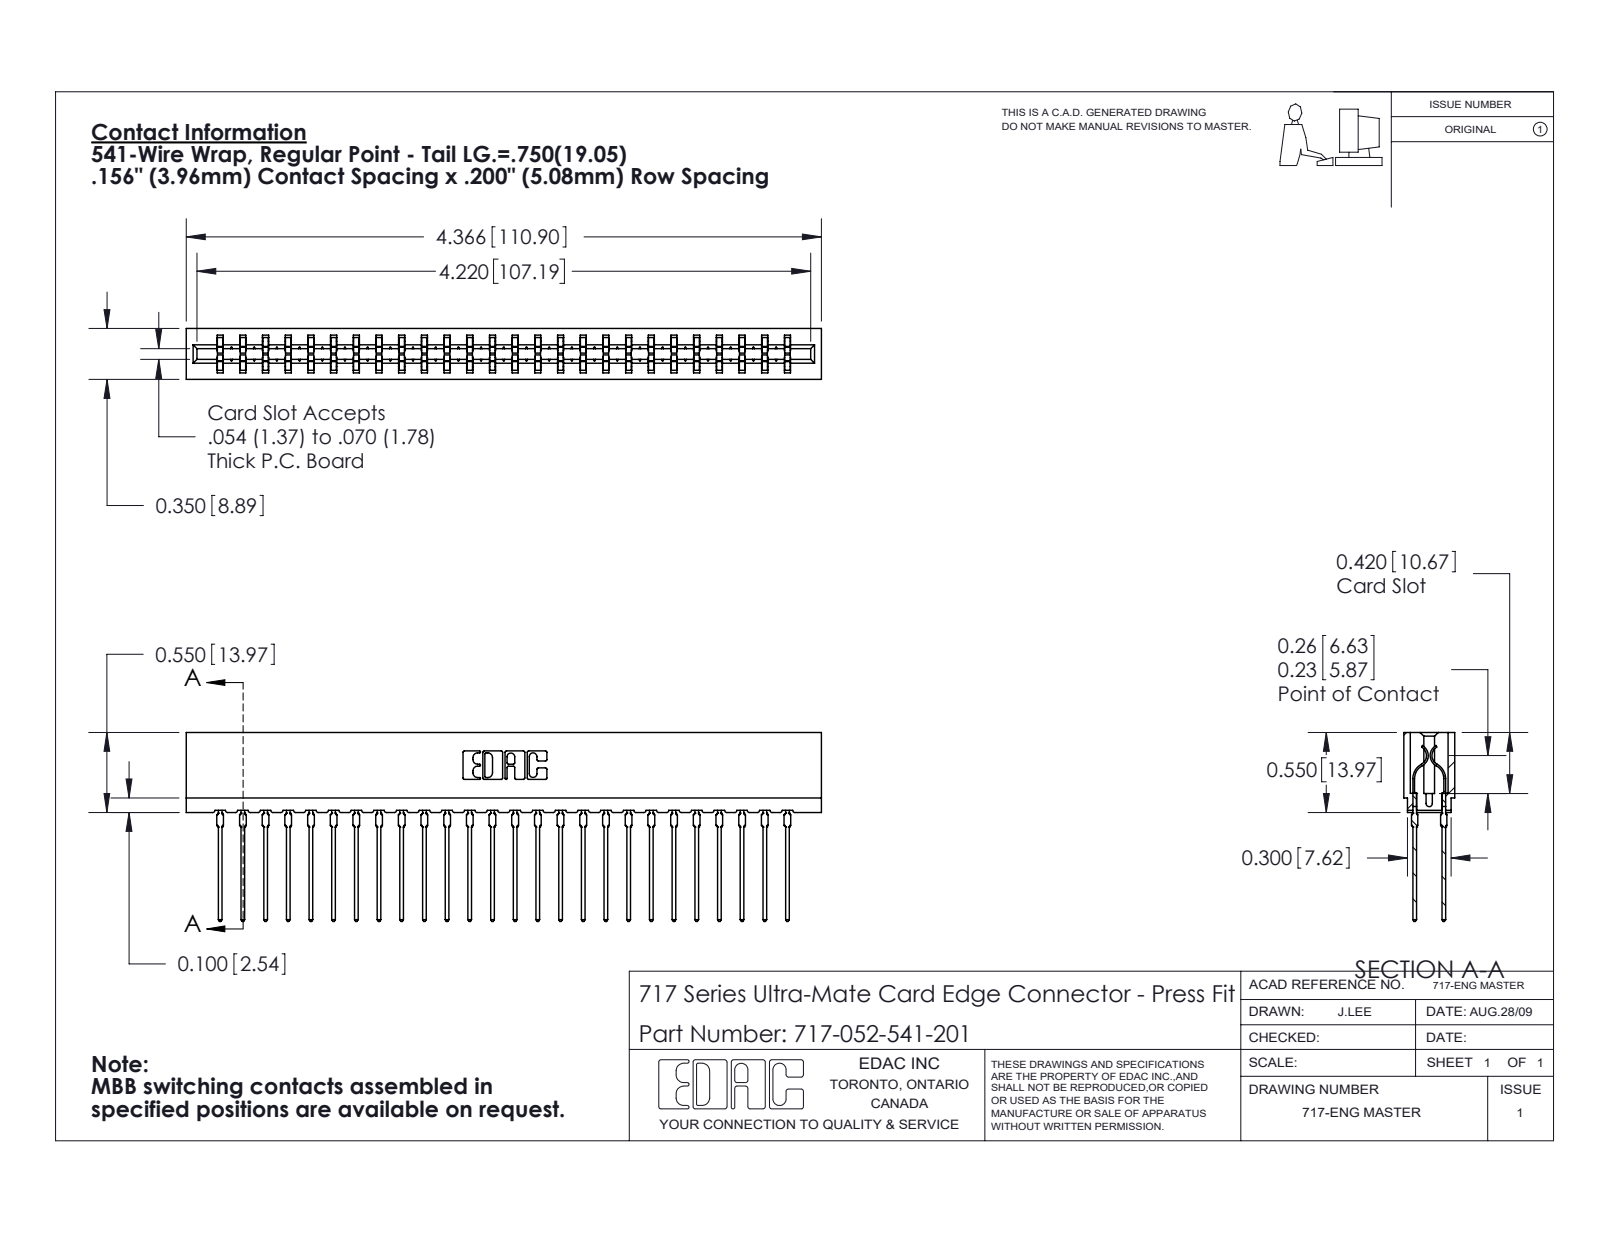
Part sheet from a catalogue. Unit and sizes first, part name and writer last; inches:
Units: inches
Overall size (bounding box): 4.366 × 1.299 × 0.35
Partial cylindrical surfaces — rounded edges, fillets, slot ends (radius × count): R0.021 ×104, R0.015 ×52, R0.01 ×22, R0.005 ×8, R0.011 ×8, R0.007 ×6, R0.031 ×6, R0.026 ×3
Main face-to-face distances: 0.212, 0.138, 0.35, 0.063, 0.287, 0.076, 0.149, 0.087, 0.263, 0.025
Volume: 0.606 in³ · Surface area: 25.01 in²
Bodies: 53 solids, 4774 faces (2472 planar, 950 cylindrical, 1352 other)
Part name (STEP PRODUCT): 717-052-541-201; 717 Part_Insulator Option - 06; 745-292-001_541
STEP written by: SolidWorks 2020 (CONFIG_CONTROL_DESIGN)
